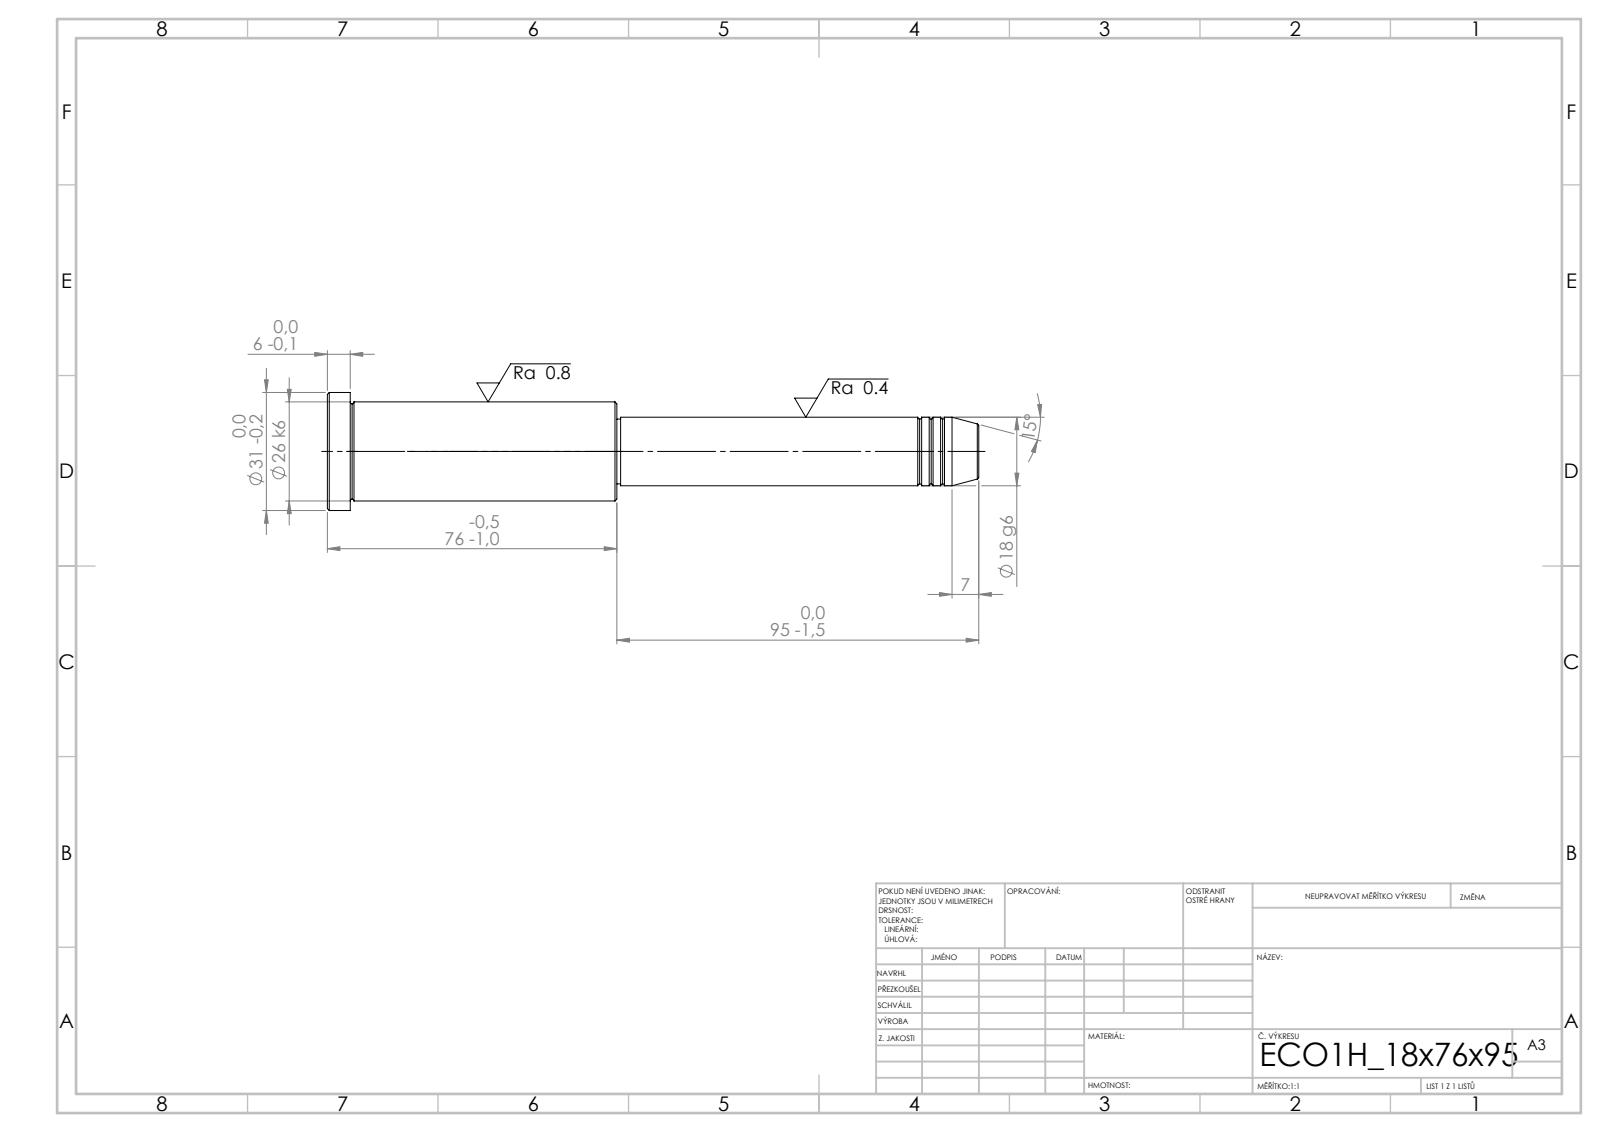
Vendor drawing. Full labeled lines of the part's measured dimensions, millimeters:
STEP written by: SolidWorks 2019 (CONFIG_CONTROL_DESIGN)
Units: millimetres
Bodies: 1 solid, 43 faces (5 planar, 14 cylindrical, 24 other)
Overall size (bounding box): 171 × 31 × 31
Volume: 65 375 mm³ · Surface area: 13 184 mm²
Round bosses / shafts (diameter × count): ⌀31 ×1, ⌀26 ×1, ⌀18 ×1, ⌀17 ×1
Main face-to-face distances: 76, 70, 6, 95, 165, 171, 94, 1, 71, 77
